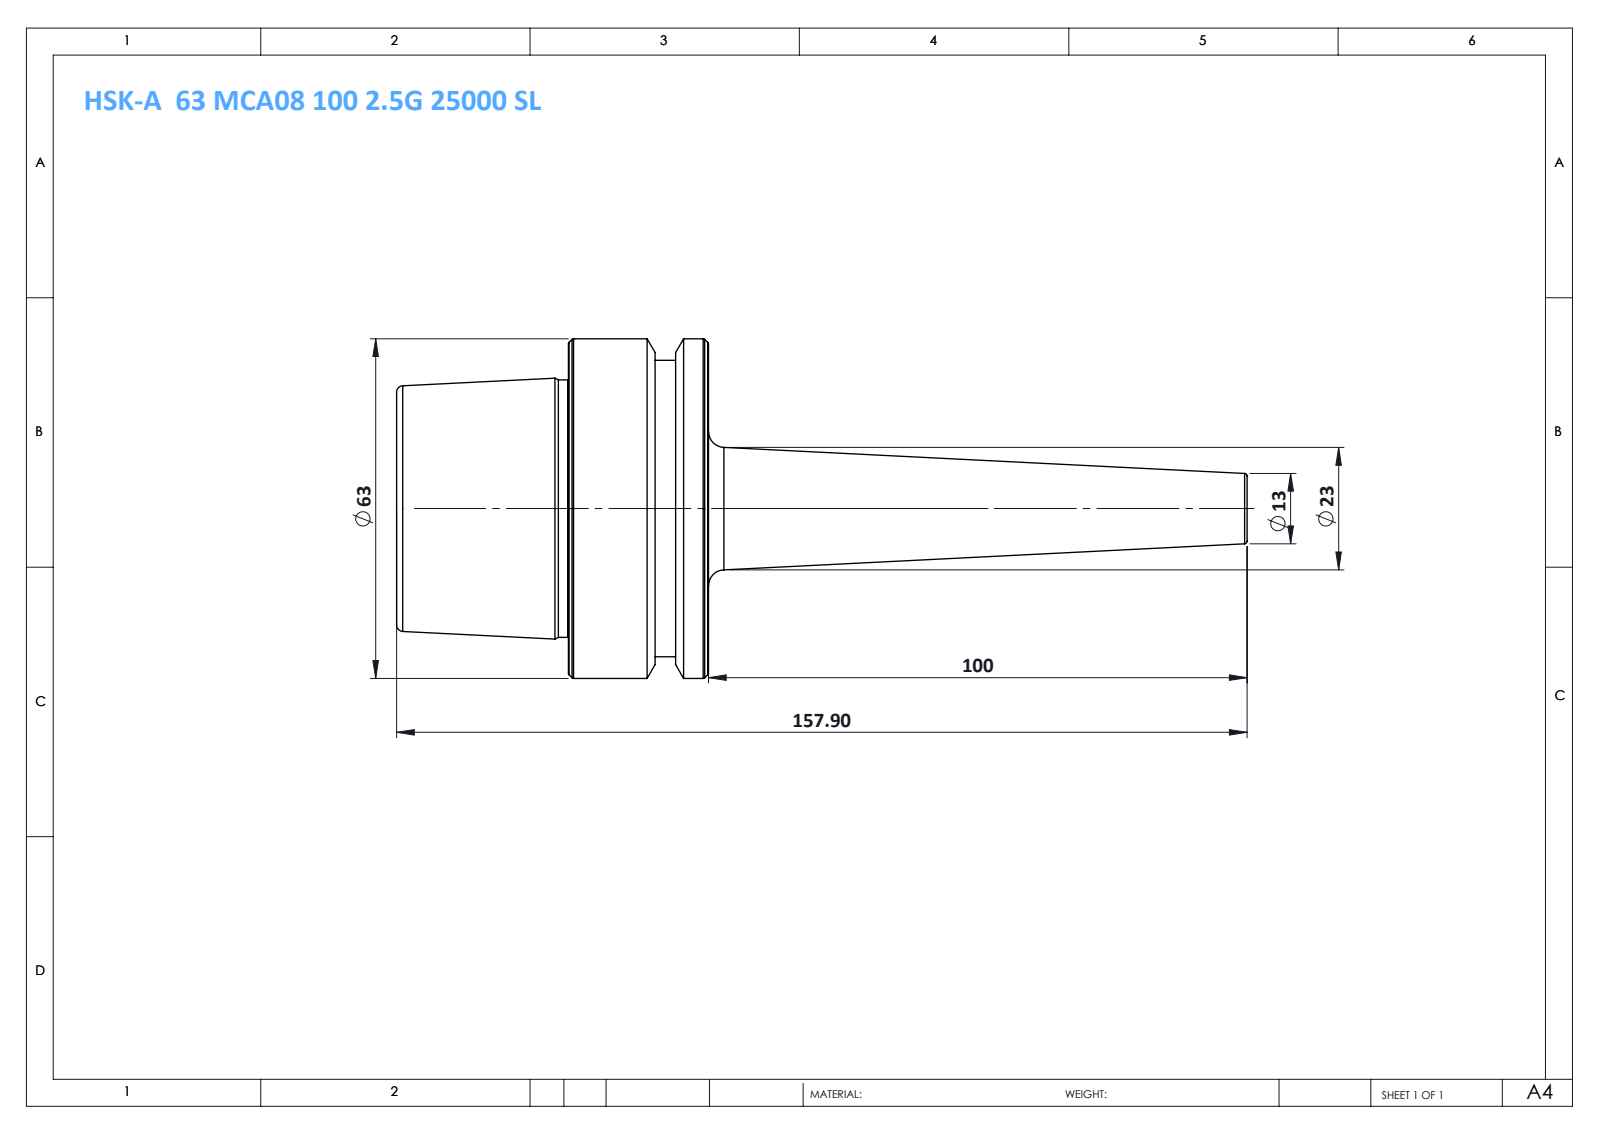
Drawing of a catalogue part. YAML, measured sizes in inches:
part_name: "HSK-A 63 MCA08 100 2.5G 25000 SL"
step_written_by: "SolidWorks 2014 (CONFIG_CONTROL_DESIGN)"
units: inches
bodies: {solids: 1, faces: 46, planar: 6, cylindrical: 8, other: 32}
overall_size: [6.217, 2.48, 2.48]
volume: 9.692
surface_area: 34.01
round_bosses_or_shafts:
  - {diameter: 2.48, count: 1}
  - {diameter: 2.165, count: 1}
  - {diameter: 1.881, count: 1}
face_to_face_distances: [2.28, 1.024, 1.256, 0.24, 0.783, 2.039, 0.39, 0.15, 0.634, 1.89]
